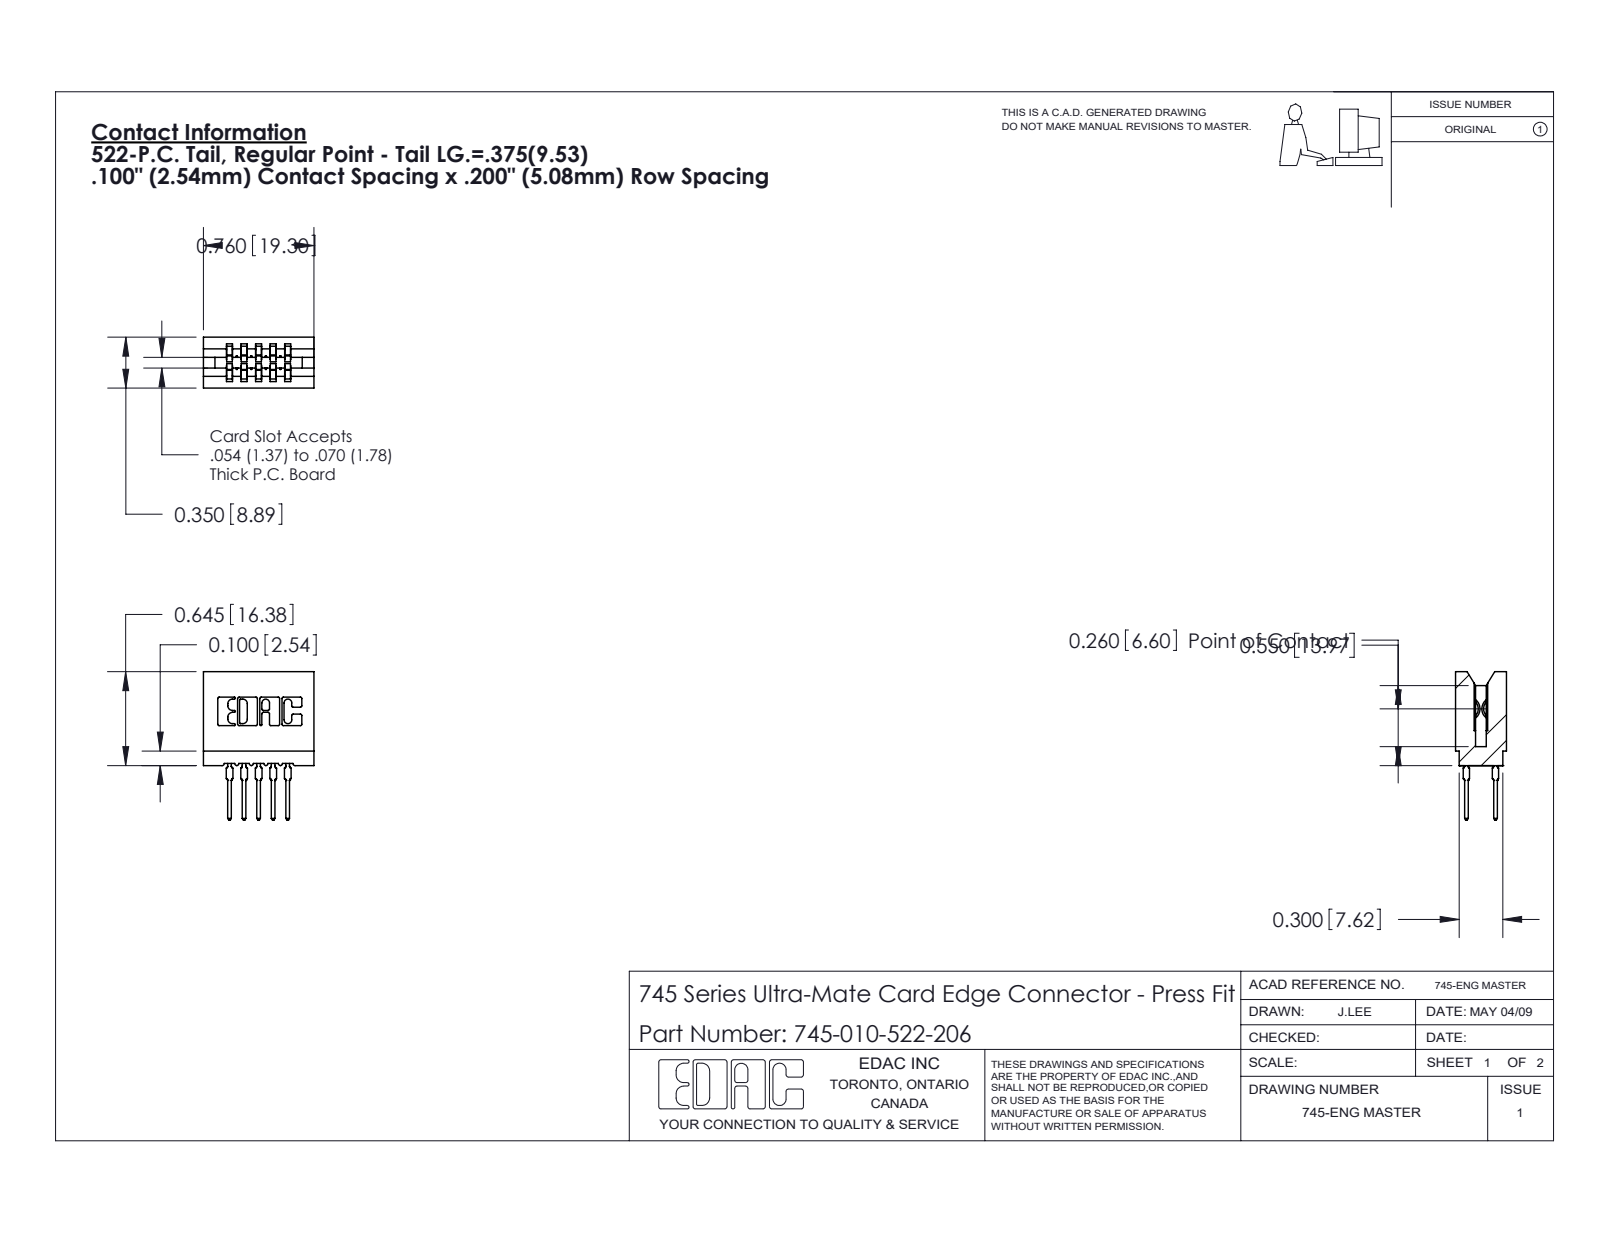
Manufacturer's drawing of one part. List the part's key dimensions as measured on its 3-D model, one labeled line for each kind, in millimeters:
Part name (STEP PRODUCT): 745 Part_Insulator Option - 06; 745-292-001_522; 745-010-522-206
STEP written by: SolidWorks 2020 (CONFIG_CONTROL_DESIGN)
Units: millimetres
Bodies: 11 solids, 991 faces (516 planar, 215 cylindrical, 260 other)
Overall size (bounding box): 25.9 × 19.3 × 8.9
Volume: 1 950 mm³ · Surface area: 3 170 mm²
Partial cylindrical surfaces — rounded edges, fillets, slot ends (radius × count): R0.3 ×22, R0.5 ×20, R0.4 ×10, R0.1 ×8, R0.3 ×8, R0.2 ×6, R0.8 ×6, R0.7 ×3
Main face-to-face distances: 2.5, 5.1, 1.1, 7.6, 3.6, 1.5, 8.9, 6.1, 4, 3.5
